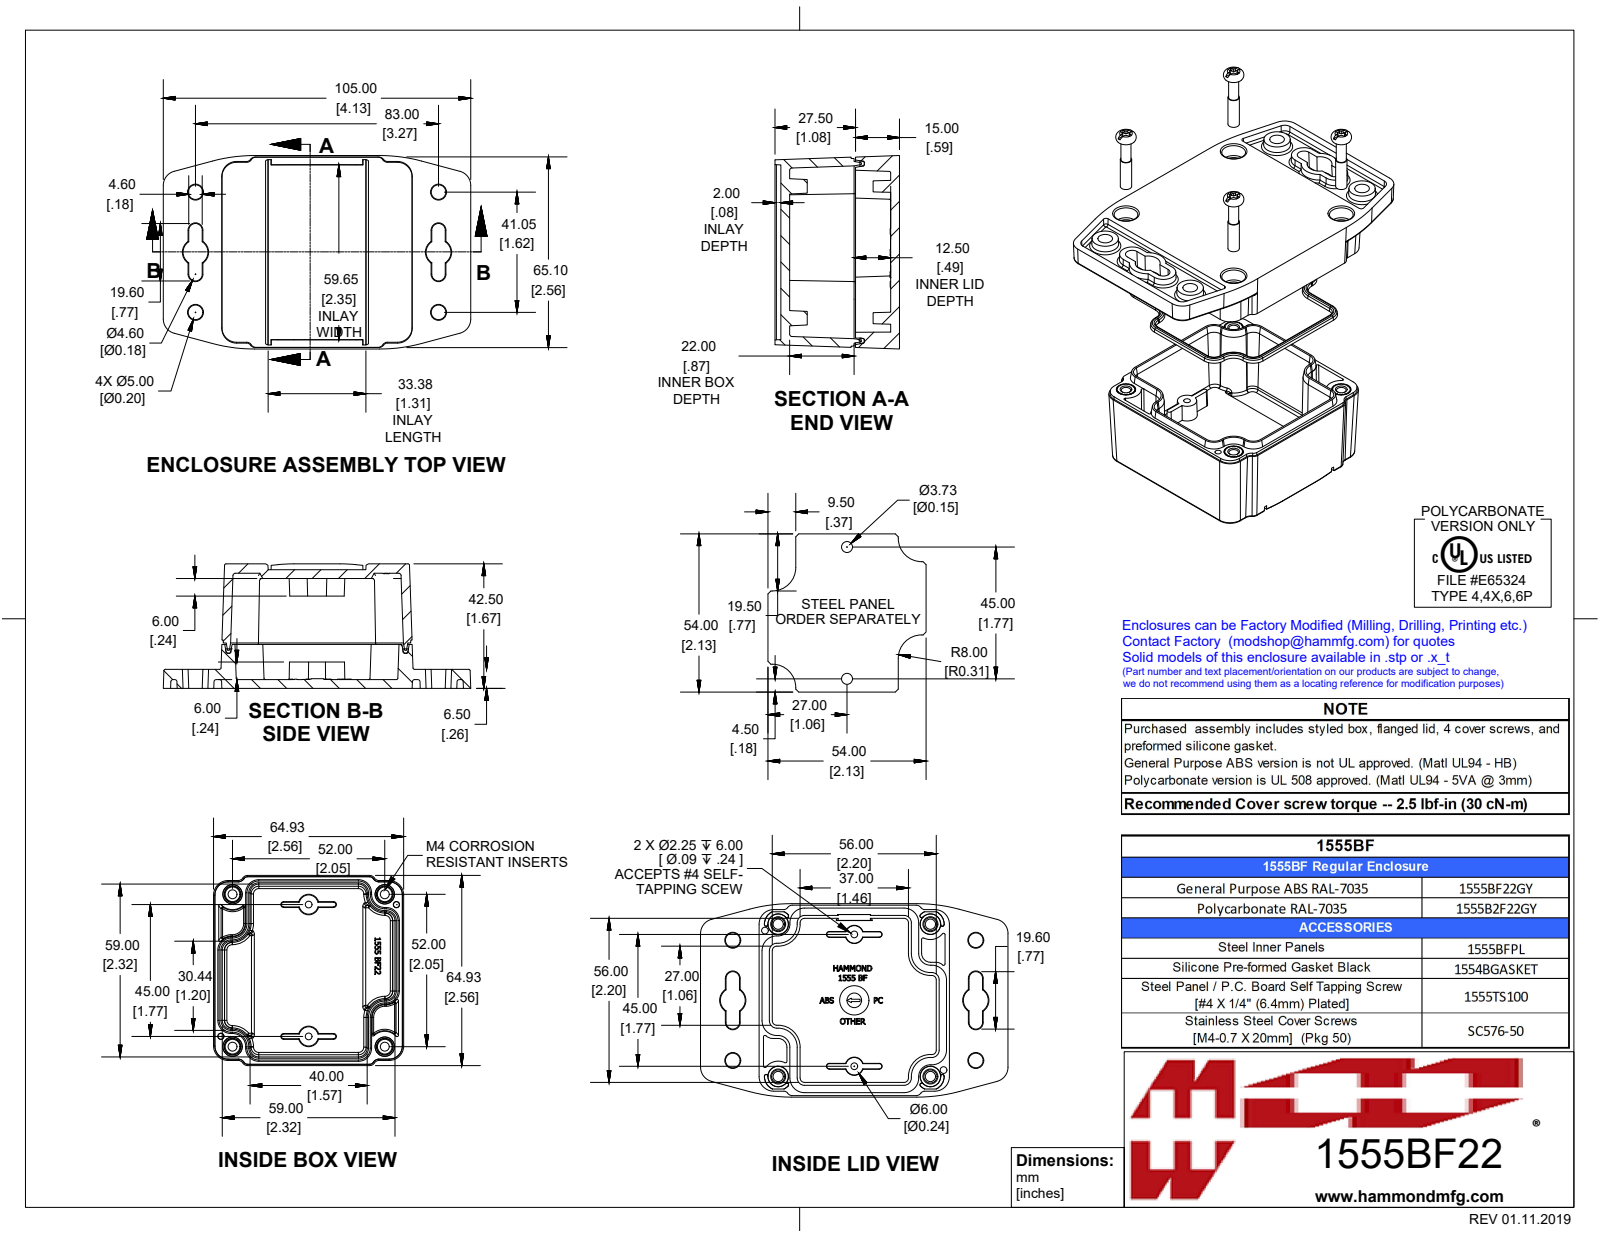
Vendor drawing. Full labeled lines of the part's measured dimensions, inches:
Part name (STEP PRODUCT): 1555B2F22GY
STEP written by: SolidWorks 2019 (AUTOMOTIVE_DESIGN)
Units: inches
Bodies: 11 solids, 1541 faces (373 planar, 340 cylindrical, 828 other)
Overall size (bounding box): 4.134 × 2.6 × 1.673
Volume: 4.563 in³ · Surface area: 82.43 in²
Round holes (diameter × count): ⌀0.128 ×4, ⌀0.091 ×2
Round bosses / shafts (diameter × count): ⌀0.25 ×4, ⌀0.218 ×4, ⌀0.21 ×4, ⌀0.153 ×4, ⌀0.135 ×4
Partial cylindrical surfaces — rounded edges, fillets, slot ends (radius × count): R0.02 ×76, R0.031 ×22, R0.03 ×12, R0.197 ×8, R0.004 ×6, R2.185 ×4, R2.165 ×2
Main face-to-face distances: 0.118, 1.476, 0.079, 0.138, 0.117, 1.358, 1.594, 0.256, 0.197, 1.22
Hole centre spacings: 1.033, 2.047, 2.167, 2.895, 1.772
